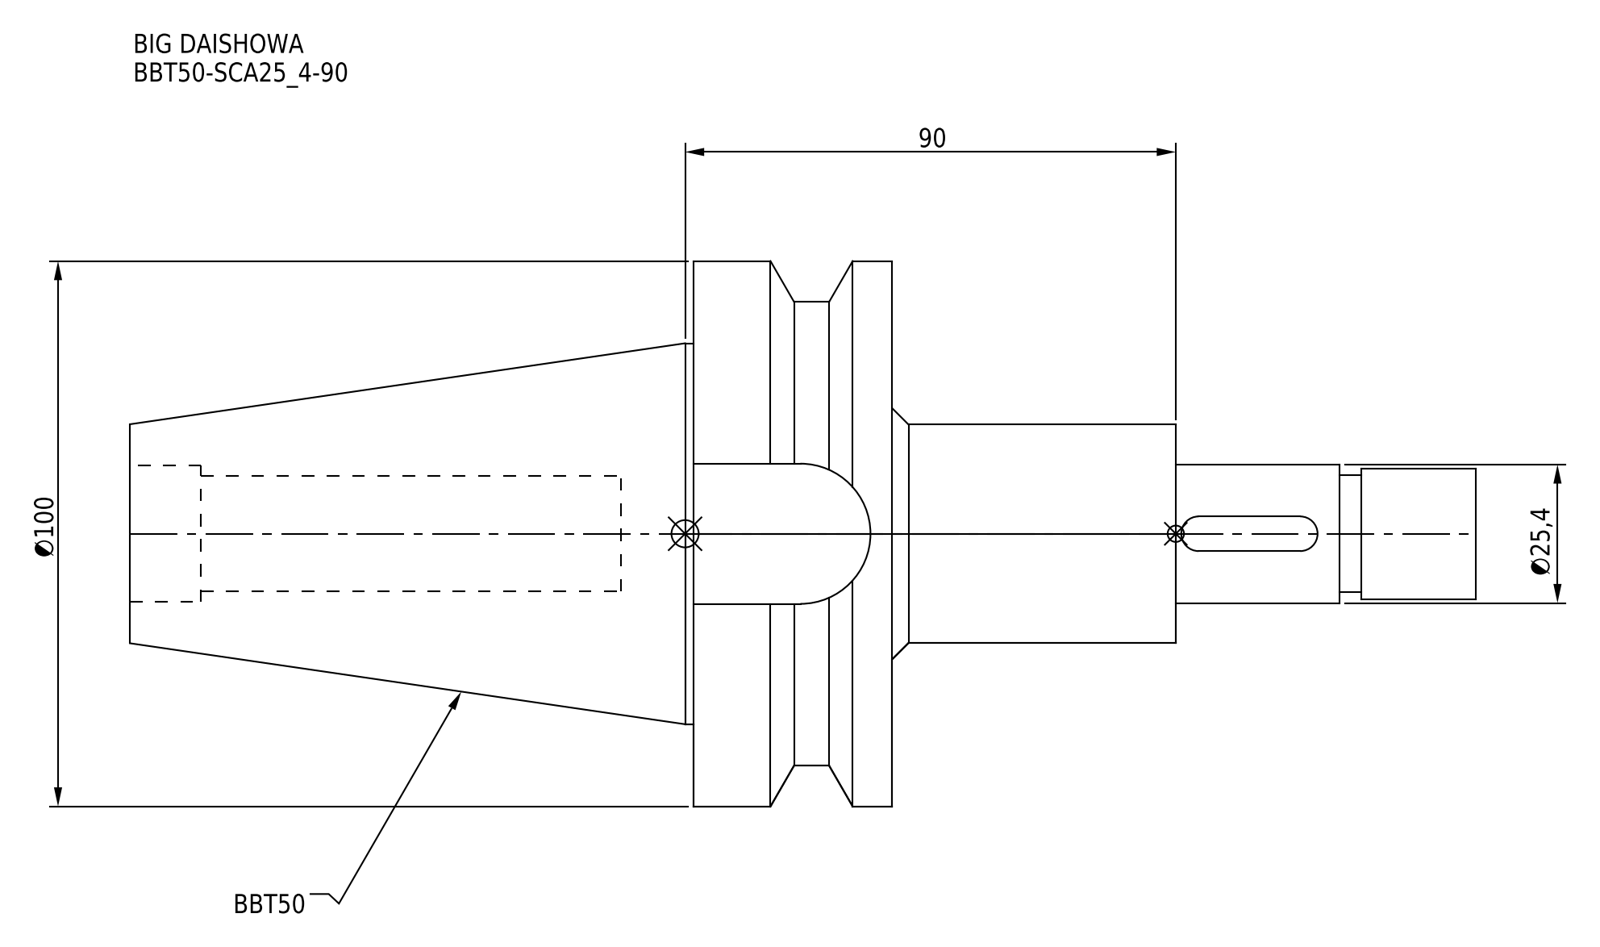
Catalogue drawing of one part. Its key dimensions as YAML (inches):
part_name: "BBT50-SCA25_4-90"
step_written_by: "CREO PARAMETRIC BY PTC INC, 2016380 (AUTOMOTIVE_DESIGN)"
units: inches
bodies: {solids: 1, faces: 42, planar: 12, cylindrical: 22, other: 8}
overall_size: [9.717, 3.937, 3.937]
volume: 35.11
surface_area: 95.75
round_holes:
  - {diameter: 0.835, count: 1}
  - {diameter: 0.984, count: 1}
round_bosses_or_shafts:
  - {diameter: 3.937, count: 1}
  - {diameter: 3.346, count: 1}
  - {diameter: 2.75, count: 1}
  - {diameter: 1.575, count: 1}
  - {diameter: 1, count: 1}
  - {diameter: 0.945, count: 1}
  - {diameter: 0.846, count: 1}
partial_cylinders:
  - {radius: 0.125, count: 2}
face_to_face_distances: [1.437, 5.504, 4.067, 2.047, 3.484, 7.551, 2.165, 4.213, 5.65, 9.717]
